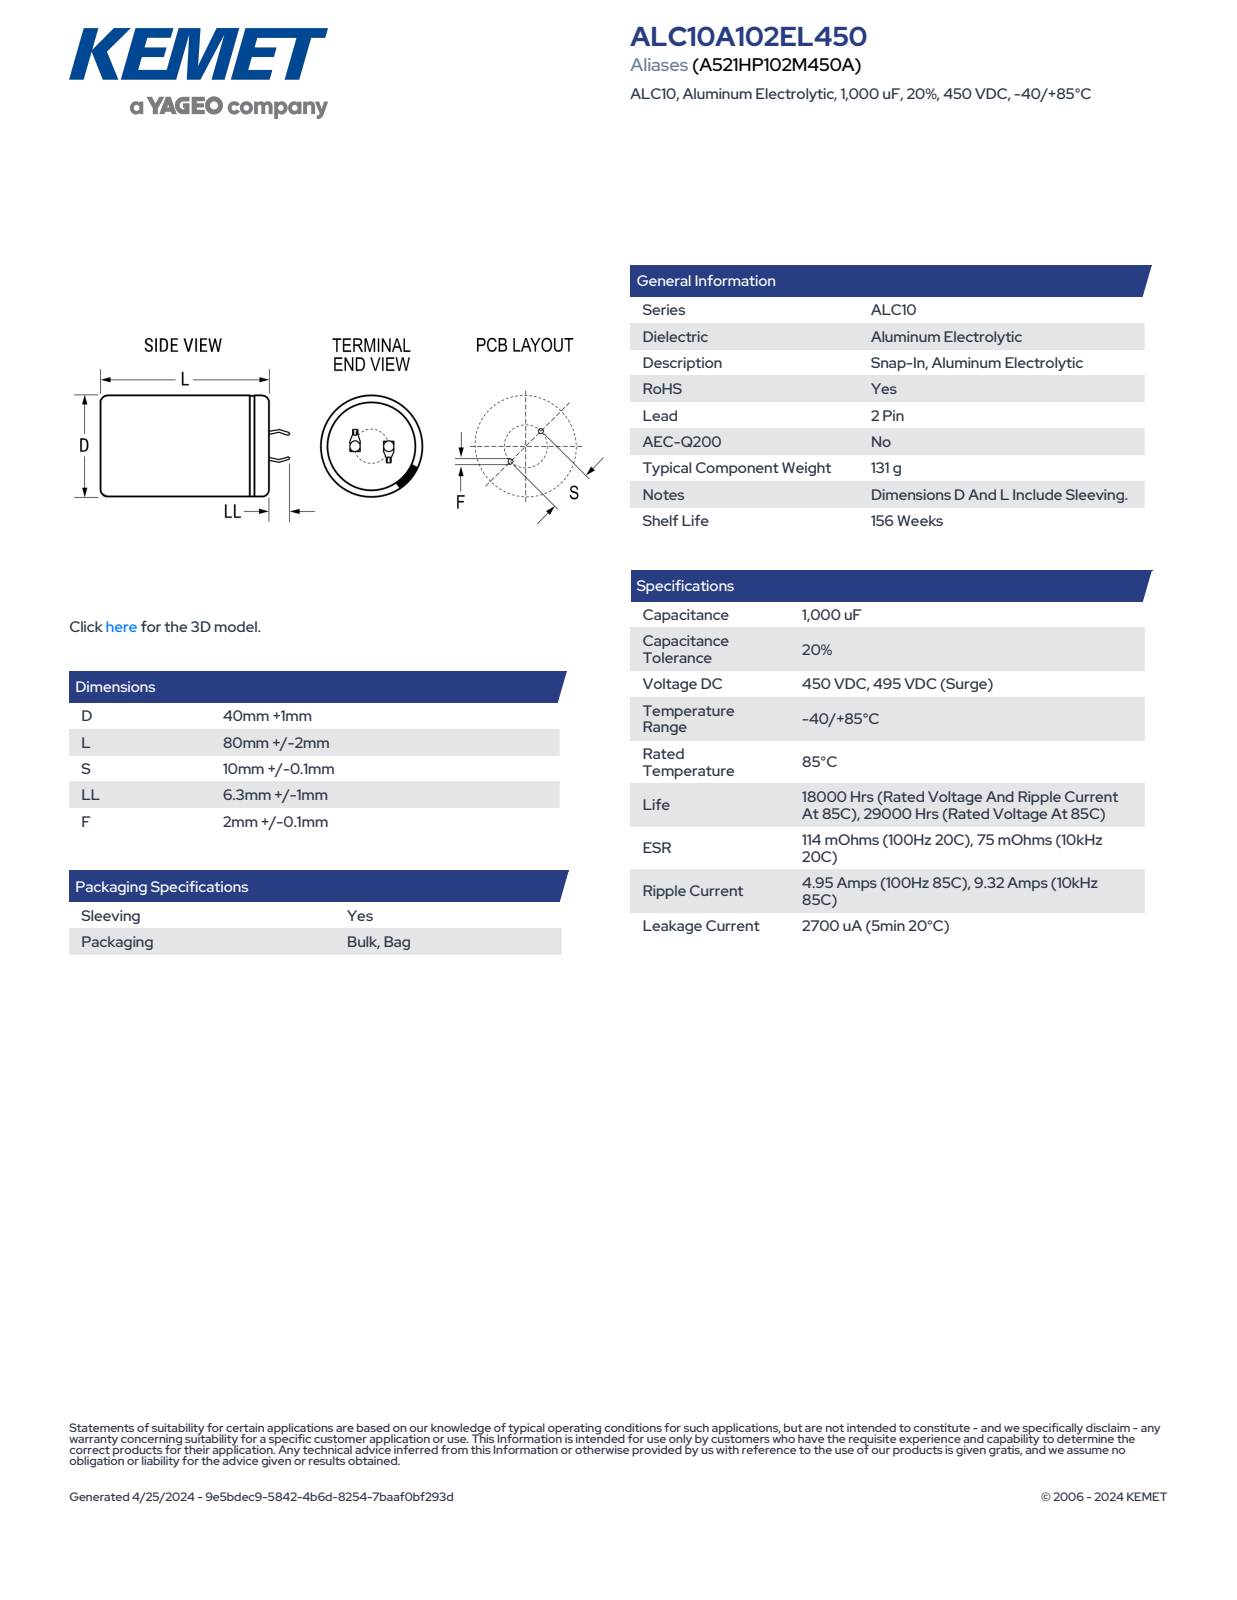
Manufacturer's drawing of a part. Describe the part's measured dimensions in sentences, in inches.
The part is named "CARS_K2P_40X80_D41L82S10LL7.3F2.1". Its 3-D file was written by "SolidWorks 2014 (AUTOMOTIVE_DESIGN)". It is 1 solid with 100 faces: 52 planar, 9 cylindrical and 39 other. Overall it measures 3.515 by 1.614 by 1.614 inches. Its volume is 6.559 cubic inches and its surface area 20.44 square inches. Round holes: 1 of diameter 1.428. Round bosses or shafts: 1 of diameter 1.614. Partial cylindrical surfaces (rounded edges, fillets, slot ends): 1 of radius 0.807. The main face-to-face distances are 3.228, 0.024, 3.248, 0.02, 0.279, 0.301, 0.03, 0.053, 0.302, 0.255.
